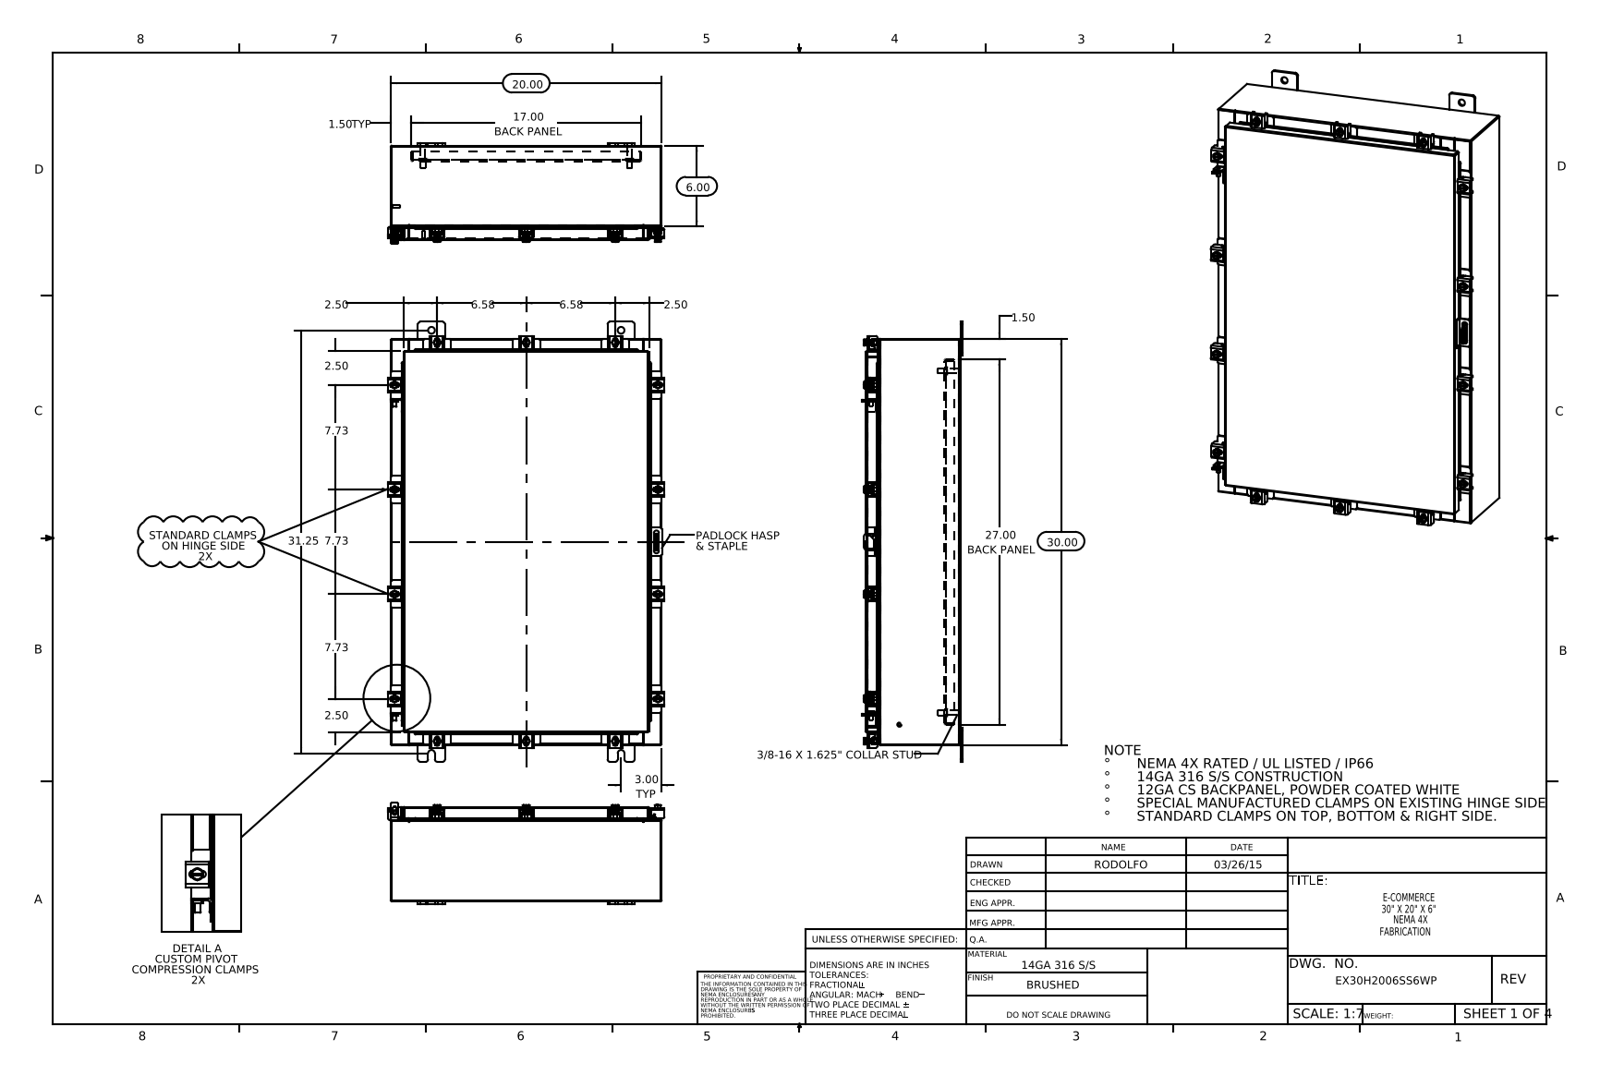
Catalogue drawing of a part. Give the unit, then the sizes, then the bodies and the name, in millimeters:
Units: millimetres
Overall size (bounding box): 825.5 × 518.7 × 189.3
Round holes (diameter × count): ⌀5.4 ×14, ⌀6.6 ×14, ⌀12.7 ×8, ⌀3.2 ×1, ⌀6.4 ×1
Round bosses / shafts (diameter × count): ⌀12.7 ×14, ⌀6.4 ×14, ⌀10.1 ×12, ⌀15.9 ×4, ⌀9.5 ×4, ⌀8.4 ×4, ⌀8 ×2, ⌀6 ×2
Partial cylindrical surfaces — rounded edges, fillets, slot ends (radius × count): R1.5 ×62, R3.6 ×28, R0.3 ×26, R3 ×26, R4.8 ×24, R2.2 ×22, R2.3 ×20, R1.3 ×19
Main face-to-face distances: 1.9, 175.3, 177.2, 173.4, 2.6, 25.4, 27.3, 148, 149.9, 29.9
Hole centre spacings: 59.6, 112.8, 421.7, 494.1, 617.5, 673.3, 695.2, 756.7
Volume: 3 507 000 mm³ · Surface area: 3 420 000 mm²
Bodies: 91 solids, 2272 faces (1211 planar, 885 cylindrical, 176 other)
Part name (STEP PRODUCT): ATEX CLAMP HINGE BRAKET; EX30H2006SS6WP Clamp Bracket; EX30H2006SS6WP Standard Clamps; EX30H2006SS6WP Top (+8 more)
STEP written by: SolidWorks 2014 (CONFIG_CONTROL_DESIGN)
